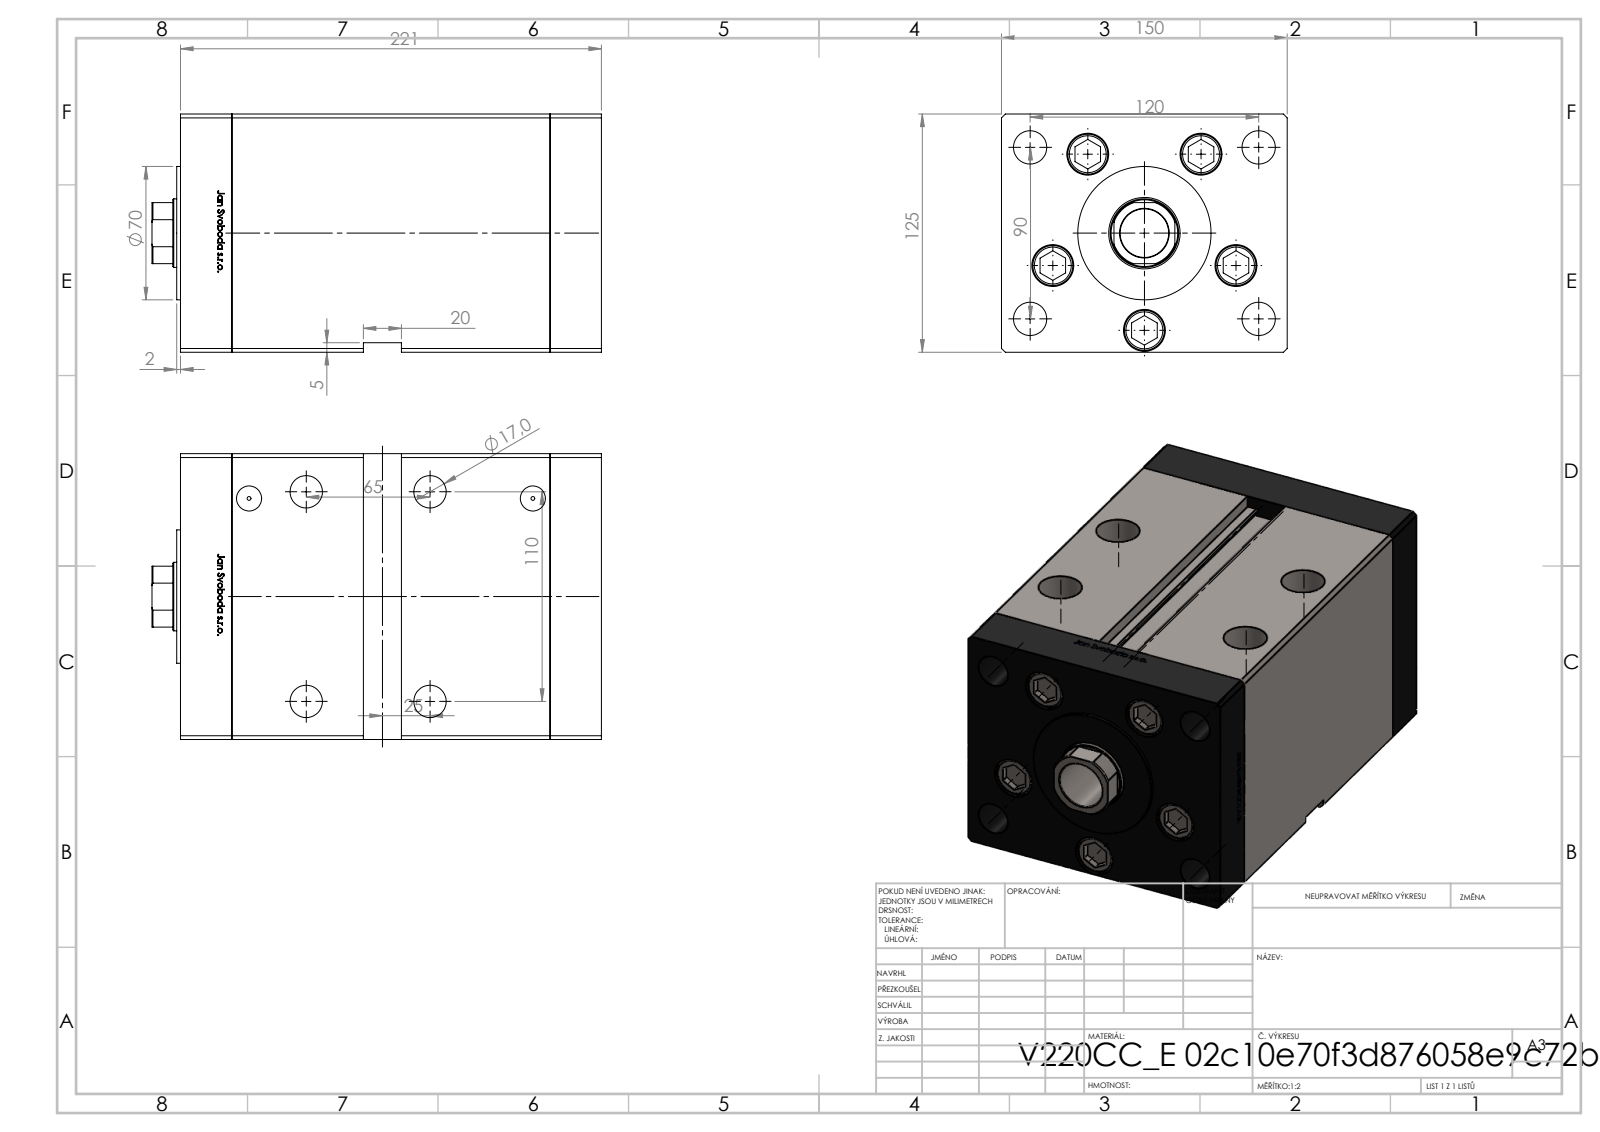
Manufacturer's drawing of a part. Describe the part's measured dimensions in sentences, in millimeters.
The part is named "ALLEN BOLT; V220C_E MIDDLE; V220C_VC_E; V220C BACK_E (+1 more)". Its 3-D file was written by "SolidWorks 2019 (CONFIG_CONTROL_DESIGN)". It is 14 solids with 1214 faces: 475 planar, 165 cylindrical and 574 other. Overall it measures 236 by 150 by 125 millimeters. Its volume is 3 421 000 cubic millimeters and its surface area 396 942 square millimeters. Round holes: 9 of diameter 17.5, 5 of diameter 22, 4 of diameter 17, 4 of diameter 23, 2 of diameter 2, 2 of diameter 13.16, 1 of diameter 25.5, 1 of diameter 36, 1 of diameter 37.5. Round bosses or shafts: 5 of diameter 21, 5 of diameter 8, 1 of diameter 80, 1 of diameter 70. Partial cylindrical surfaces (rounded edges, fillets, slot ends): 2 of radius 0.93, 1 of radius 17.5. The main face-to-face distances are 27, 194, 167, 125, 150, 33.5, 6.5, 221, 160.5, 187.5. The hole center spacings are 51, 75, 30.43, 30.48, 58.89, 60.3, 61.25, 63.14.
